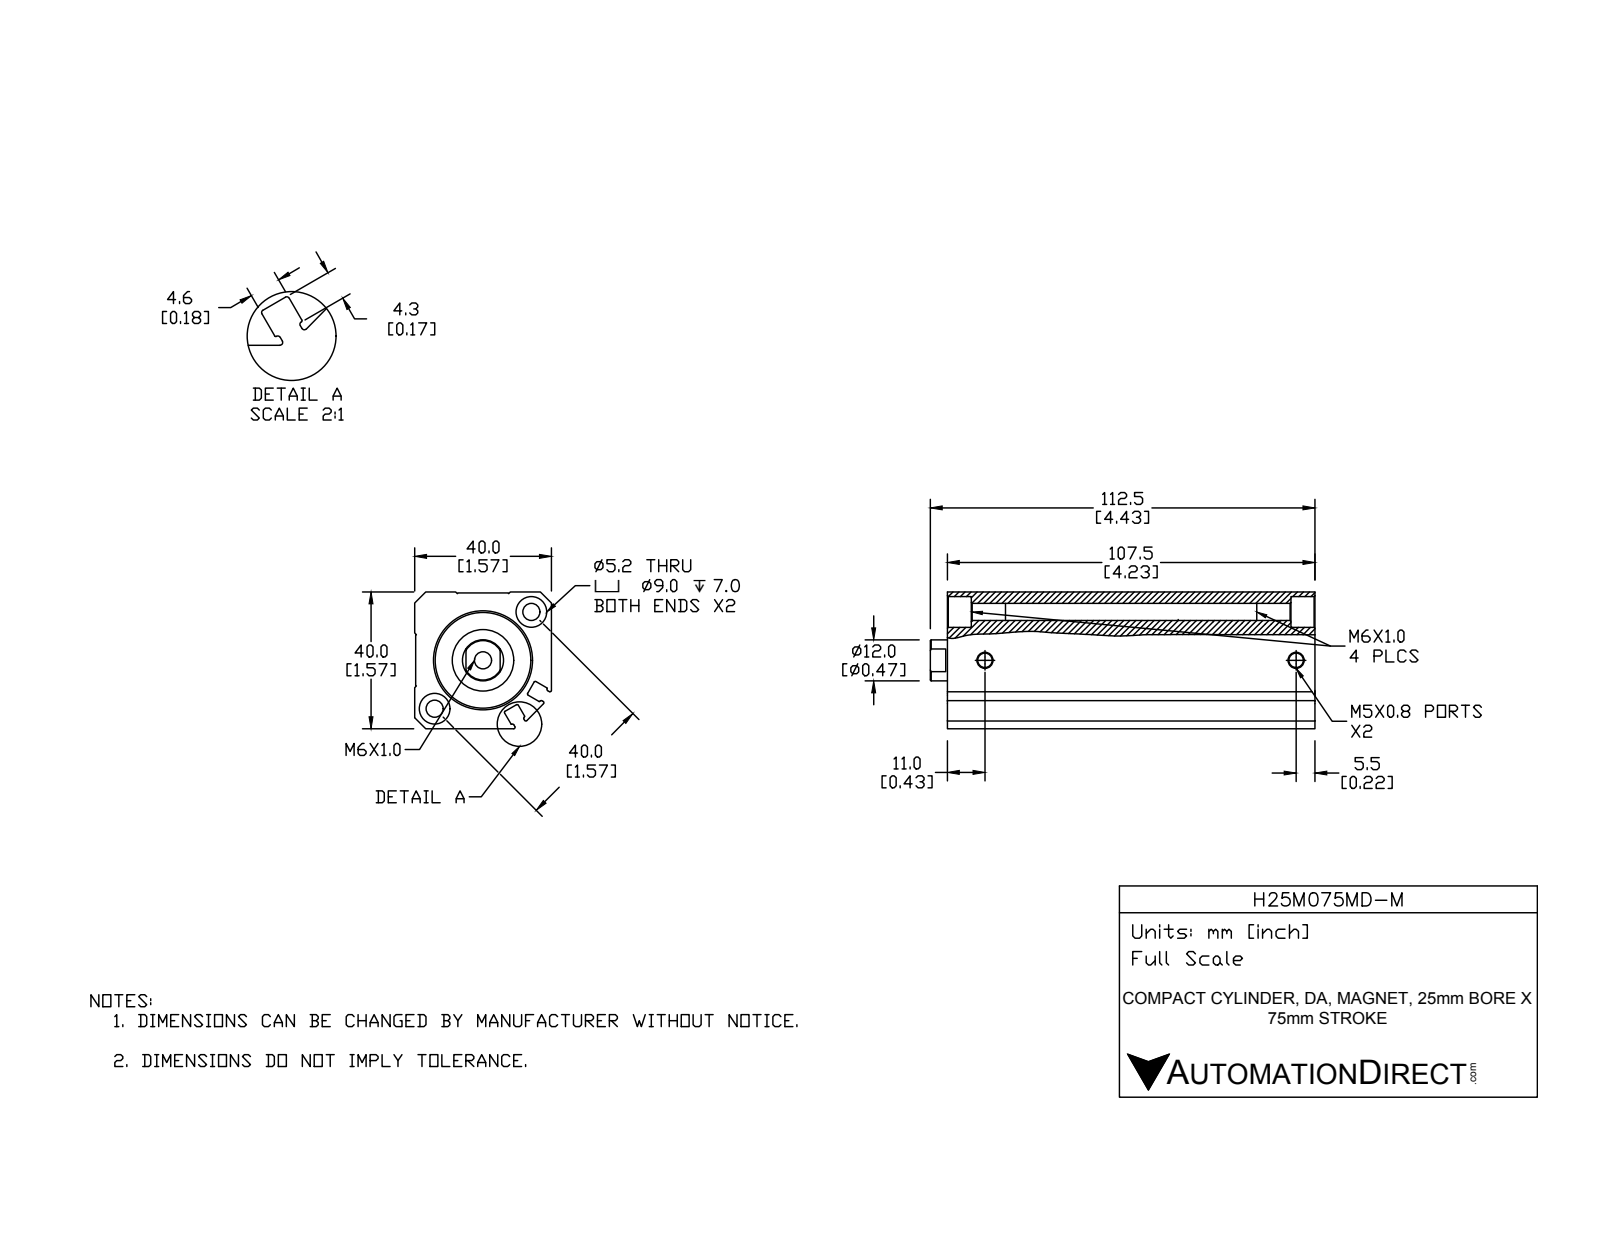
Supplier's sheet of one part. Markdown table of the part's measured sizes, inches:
| quantity | value |
| --- | --- |
| part name | H25M075MD-M-PISTON; H25M075MD-M-BODY; H25M075MD-M |
| STEP written by | SolidWorks 2015 (CONFIG_CONTROL_DESIGN) |
| units | inches |
| bodies | 2 solids, 141 faces (53 planar, 55 cylindrical, 33 other) |
| overall size | 4.429 × 1.575 × 1.575 |
| volume | 7.498 in³ |
| surface area | 62.52 in² |
| round holes (diameter × count) | 0.197 × 3, 0.165 × 2, 0.354 × 2, 0.472 × 1, 0.63 × 1, 0.984 × 1, 1.102 × 1 |
| round bosses / shafts (diameter × count) | 0.709 × 1, 0.551 × 1 |
| partial cylindrical surfaces (radius × count) | 0.016 × 12, 0.008 × 4 |
| main face-to-face distances | 1.575, 1.563, 0.157, 0.181, 4.232, 4.075, 0.055, 0.102, 4.177, 2.047 |
| hole center spacings | 0.787, 1.574, 3.583 |
